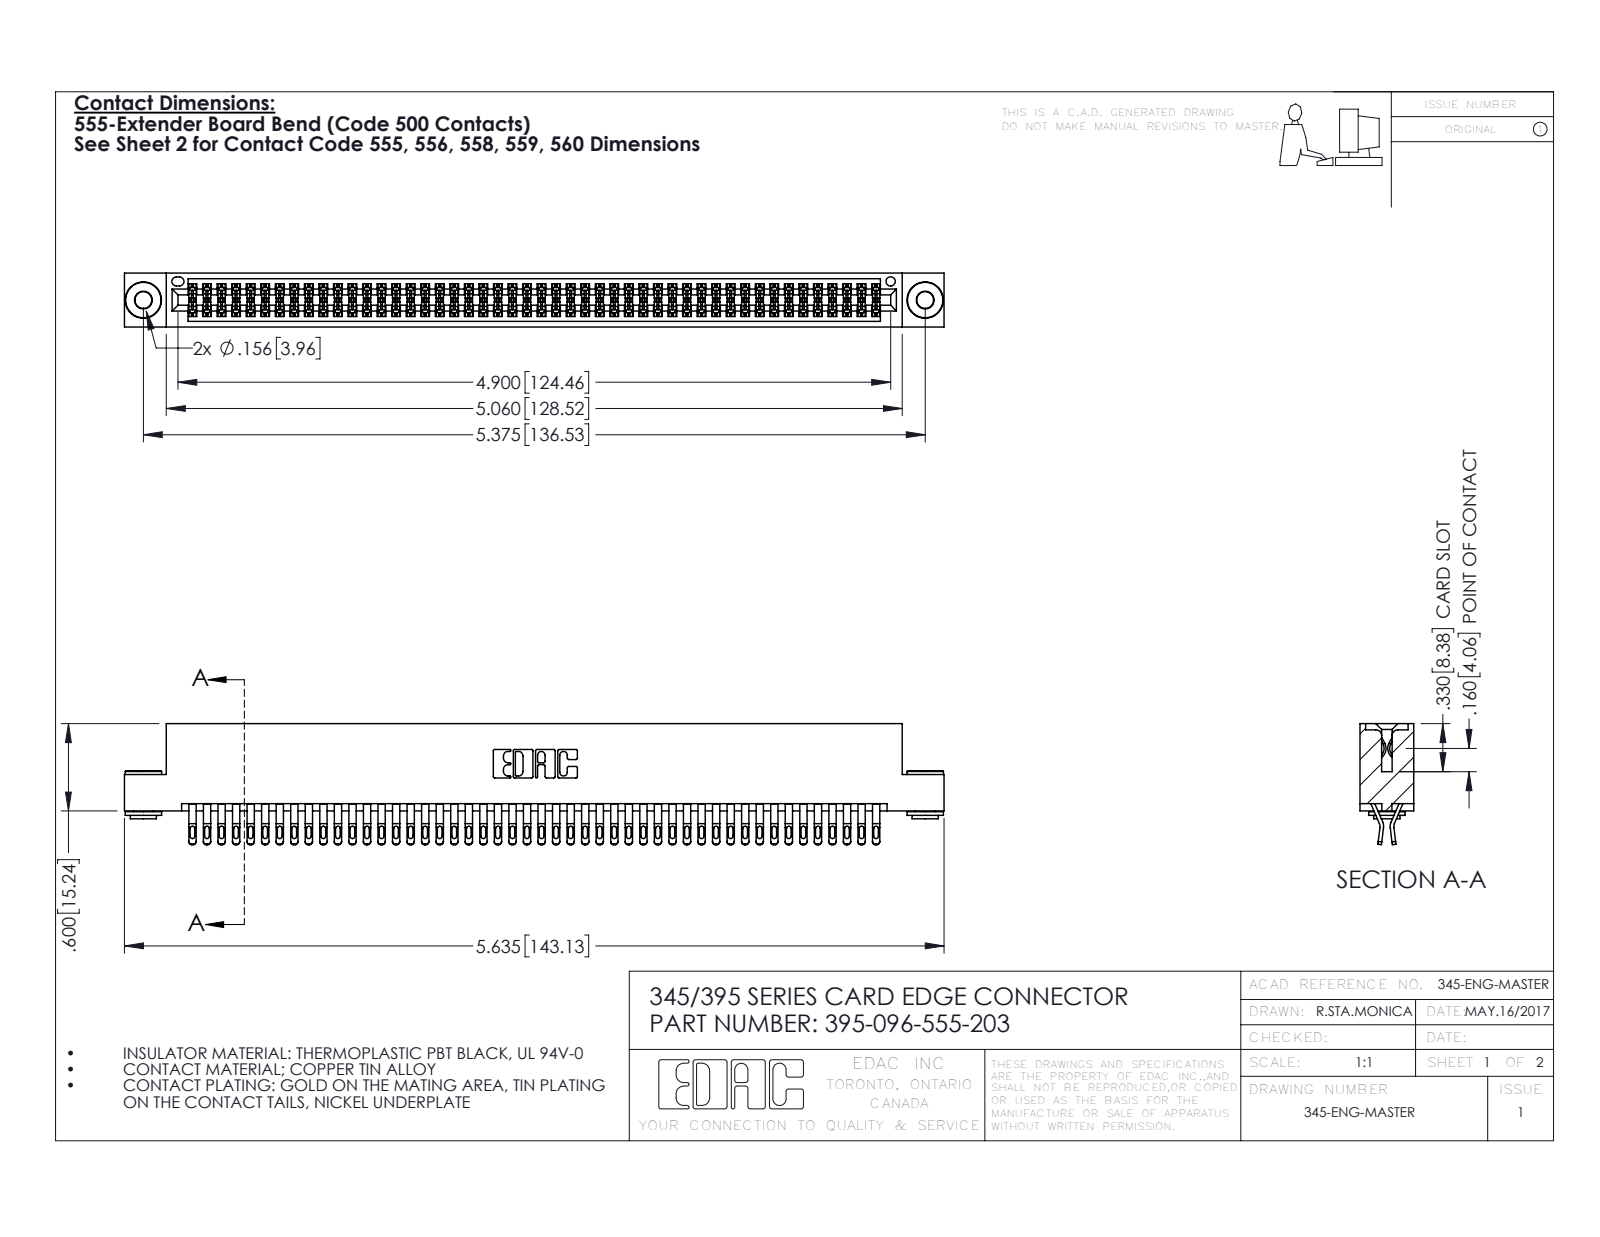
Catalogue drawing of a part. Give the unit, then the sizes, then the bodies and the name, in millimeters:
Units: millimetres
Overall size (bounding box): 143.1 × 21.1 × 9.4
Round holes (diameter × count): ⌀2.9 ×2, ⌀4 ×2, ⌀1.6 ×1
Round bosses / shafts (diameter × count): ⌀6.4 ×2, ⌀4.6 ×2, ⌀3.5 ×2
Partial cylindrical surfaces — rounded edges, fillets, slot ends (radius × count): R0.4 ×240, R0.5 ×192, R0.2 ×144, R0.3 ×22, R0.2 ×6, R0.8 ×6, R0.7 ×3, R0.3 ×2
Main face-to-face distances: 1.8, 7.6, 0.6, 9.4, 5.1, 2.5, 6.9, 5.7, 4.4, 3.8
Hole centre spacings: 6.9, 130.5, 136.5
Volume: 14 300 mm³ · Surface area: 22 360 mm²
Bodies: 99 solids, 5540 faces (3066 planar, 2466 cylindrical, 8 other)
Part name (STEP PRODUCT): 345-292-001_555 Tail; 345-250-002_345-250-002-102; 345 Part_Flush Mounting Lugs - 0.156 Dia-TH; 395-096-555-203
STEP written by: SolidWorks 2016 (CONFIG_CONTROL_DESIGN)
